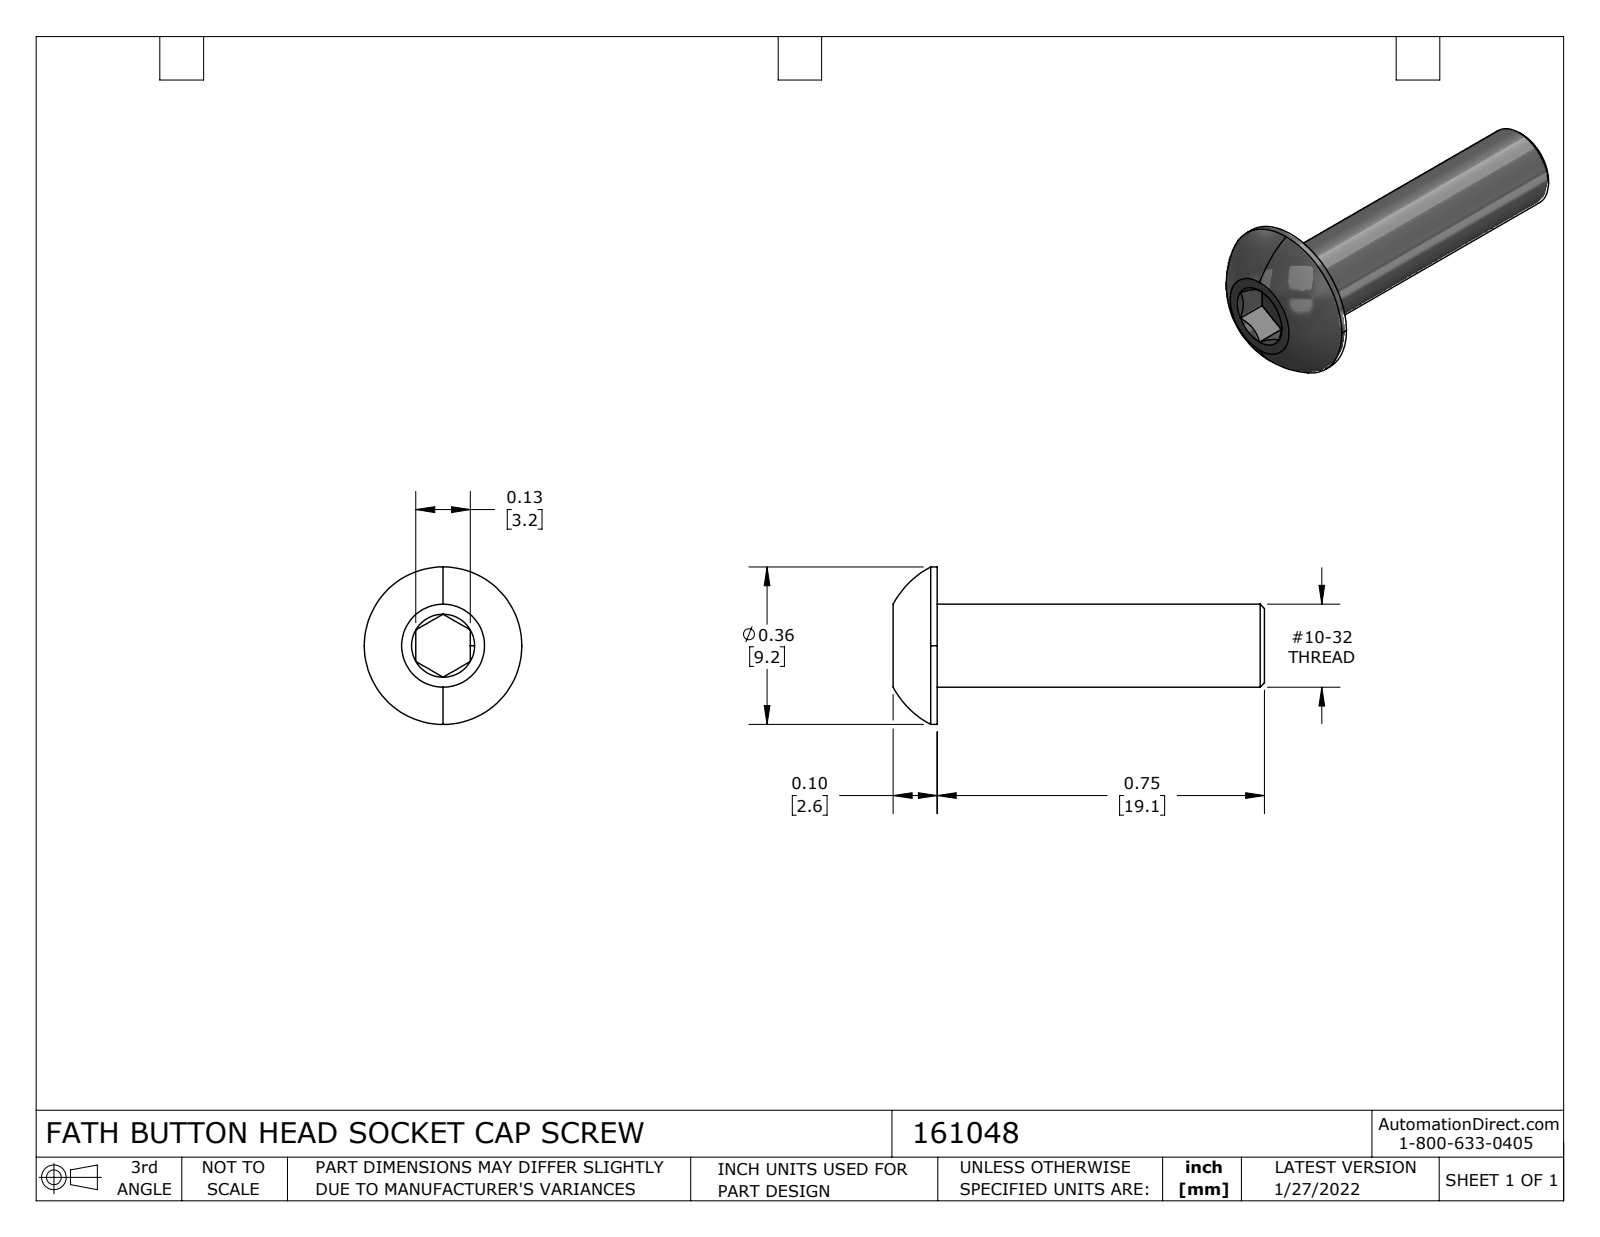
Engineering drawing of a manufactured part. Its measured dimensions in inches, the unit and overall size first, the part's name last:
Units: inches
Overall size (bounding box): 0.851 × 0.361 × 0.361
Round bosses / shafts (diameter × count): ⌀0.361 ×1, ⌀0.19 ×1
Main face-to-face distances: 0.75, 0.125, 0.78, 0.03, 0.851, 0.101, 0.071, 0.063
Volume: 0.028 in³ · Surface area: 0.731 in²
Bodies: 1 solid, 29 faces (12 planar, 4 cylindrical, 13 other)
Part name (STEP PRODUCT): 161048
STEP written by: SolidWorks 2021 (CONFIG_CONTROL_DESIGN)
